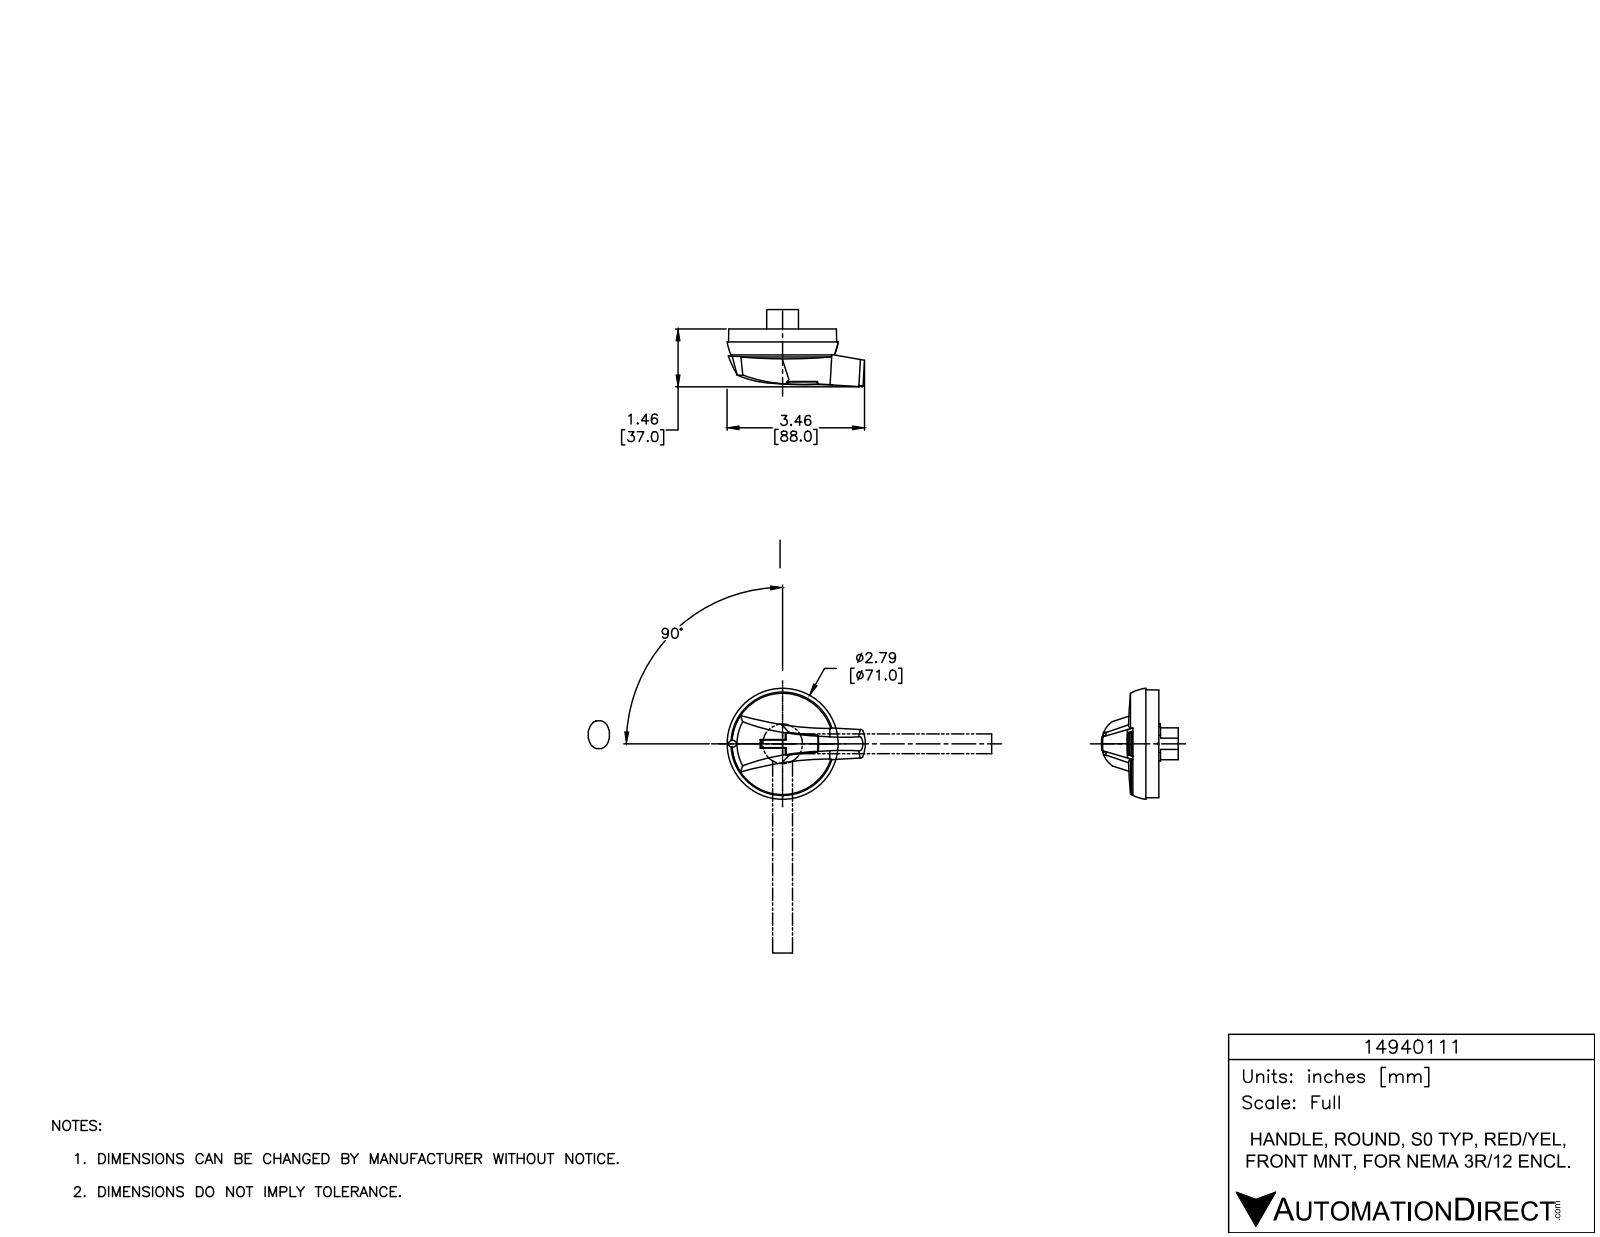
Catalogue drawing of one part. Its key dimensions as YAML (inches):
part_name: "14940111"
step_written_by: "SolidWorks 2015 (AUTOMOTIVE_DESIGN)"
units: inches
bodies: {solids: 6, faces: 2118, planar: 468, cylindrical: 373, other: 1277}
overall_size: [3.479, 2.8, 1.925]
volume: 3.457
surface_area: 93.25
round_holes:
  - {diameter: 0.169, count: 4}
  - {diameter: 0.193, count: 4}
  - {diameter: 0.394, count: 4}
  - {diameter: 0.079, count: 3}
  - {diameter: 0.13, count: 2}
  - {diameter: 0.157, count: 2}
  - {diameter: 0.335, count: 2}
  - {diameter: 0.118, count: 1}
  - {diameter: 0.126, count: 1}
  - {diameter: 0.457, count: 1}
  - {diameter: 0.89, count: 1}
  - {diameter: 2.618, count: 1}
round_bosses_or_shafts:
  - {diameter: 2.559, count: 1}
  - {diameter: 0.984, count: 1}
partial_cylinders:
  - {radius: 0.02, count: 114}
  - {radius: 0.039, count: 23}
  - {radius: 0.01, count: 19}
  - {radius: 0.012, count: 10}
  - {radius: 0.03, count: 8}
  - {radius: 0.641, count: 6}
  - {radius: 0.142, count: 4}
  - {radius: 0.187, count: 4}
face_to_face_distances: [0.059, 0.071, 0.13, 0.616, 0.053, 0.03, 0.557, 0.486, 0.152, 0.295]
hole_center_spacings: [0.564, 0.961, 1.557, 0.669, 0.677, 1.102, 1.181, 1.575]
